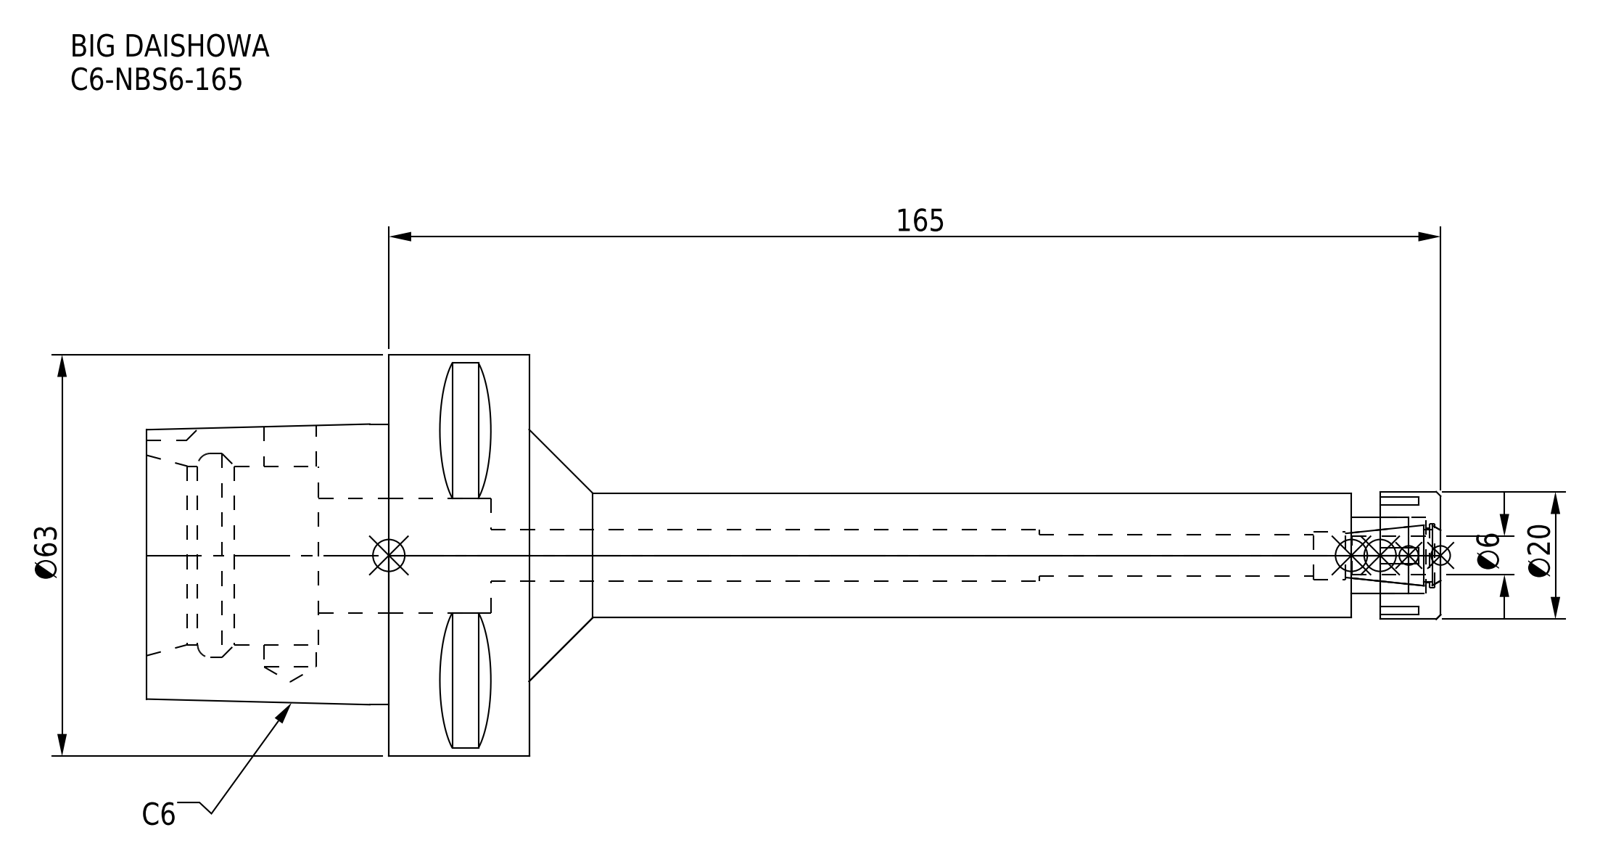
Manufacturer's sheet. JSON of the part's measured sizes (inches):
{"part_name": "DXF_TEMP_ASSY_ASM_4_ASM.stp; C6-NBS6-165.stp; C6-NBS6-165; C6-NBS6-165-FreeParts (+3 more)", "step_written_by": "SolidWorks 2019 (CONFIG_CONTROL_DESIGN)", "units": "inches", "bodies": {"solids": 2, "faces": 112, "planar": 61, "cylindrical": 33, "other": 18}, "overall_size": [7.992, 2.48, 2.48], "volume_in3": 8.28, "surface_area_in2": 51.22, "round_holes": [[0.252, 1], [0.295, 1], [0.315, 1], [0.319, 1], [0.335, 1], [0.394, 1], [0.472, 1], [0.709, 1], [1.102, 1], [1.26, 1]], "round_bosses_or_shafts": [[2.48, 1], [0.787, 1], [0.768, 1]], "partial_cylinders_radius": [[0.197, 1]], "face_to_face_distances": [0.866, 1.063, 2.362, 1.496, 1.299, 0.433, 0.98, 2.181, 0.236, 0.177]}
